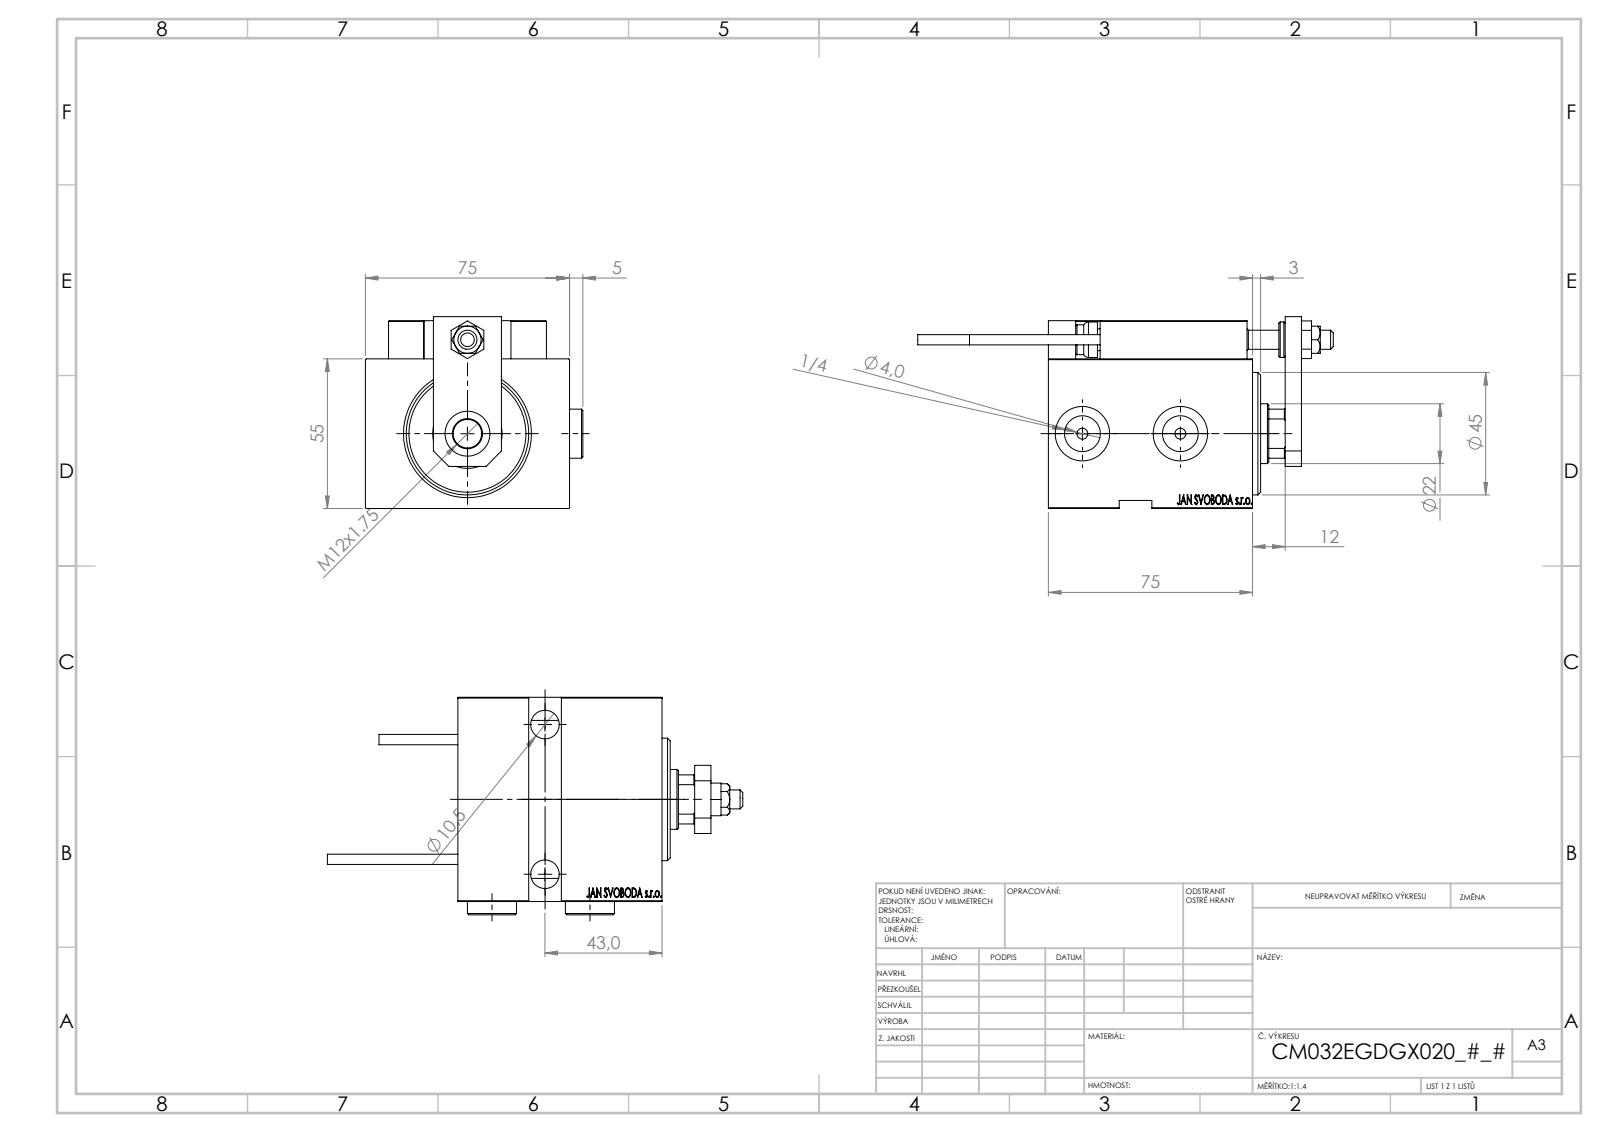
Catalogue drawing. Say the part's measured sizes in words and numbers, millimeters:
The part is named "NUT_D10; TYC_L79; V450CM_E_VCP; NUT_D12 (+7 more)". Its 3-D file was written by "SolidWorks 2019 (CONFIG_CONTROL_DESIGN)". It is 26 solids with 1336 faces: 603 planar, 188 cylindrical and 545 other. Overall it measures 152.7 by 79.9 by 70.5 millimeters. Its volume is 332 434 cubic millimeters and its surface area 80 389 square millimeters. Round holes: 6 of diameter 4, 5 of diameter 8, 4 of diameter 3.2, 3 of diameter 10.5, 3 of diameter 16.5, 2 of diameter 5, 2 of diameter 13.16, 2 of diameter 20, 1 of diameter 7, 1 of diameter 22, 1 of diameter 25.5, 1 of diameter 32. Round bosses or shafts: 2 of diameter 18, 2 of diameter 5, 2 of diameter 3.8, 1 of diameter 34, 1 of diameter 13, 1 of diameter 11. Partial cylindrical surfaces (rounded edges, fillets, slot ends): 30 of radius 0.3, 2 of radius 3, 1 of radius 10.5. The main face-to-face distances are 75, 55, 12, 3, 10, 14, 5, 25, 65, 7. The hole center spacings are 11.37, 20, 27.07, 29.59, 29.69, 32.18, 34.83, 36.06.
